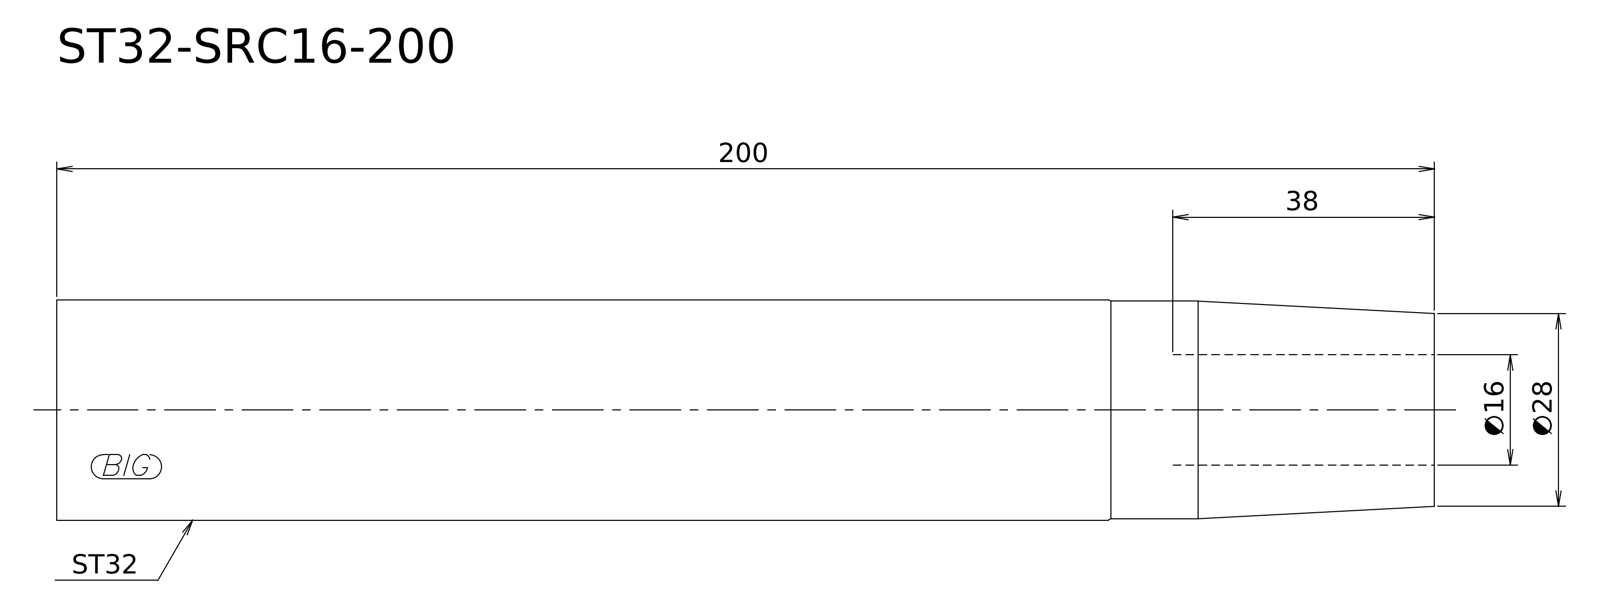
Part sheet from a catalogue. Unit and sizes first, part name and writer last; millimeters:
Units: millimetres
Overall size (bounding box): 200 × 32 × 32
Round bosses / shafts (diameter × count): ⌀32 ×1, ⌀31.6 ×1
Main face-to-face distances: 200
Volume: 156 955 mm³ · Surface area: 21 282 mm²
Bodies: 1 solid, 6 faces (2 planar, 2 cylindrical, 2 other)
STEP written by: Kubotek KeyCreator V8.5.1 (14335) (CONFIG_CONTROL_DESIGN)
